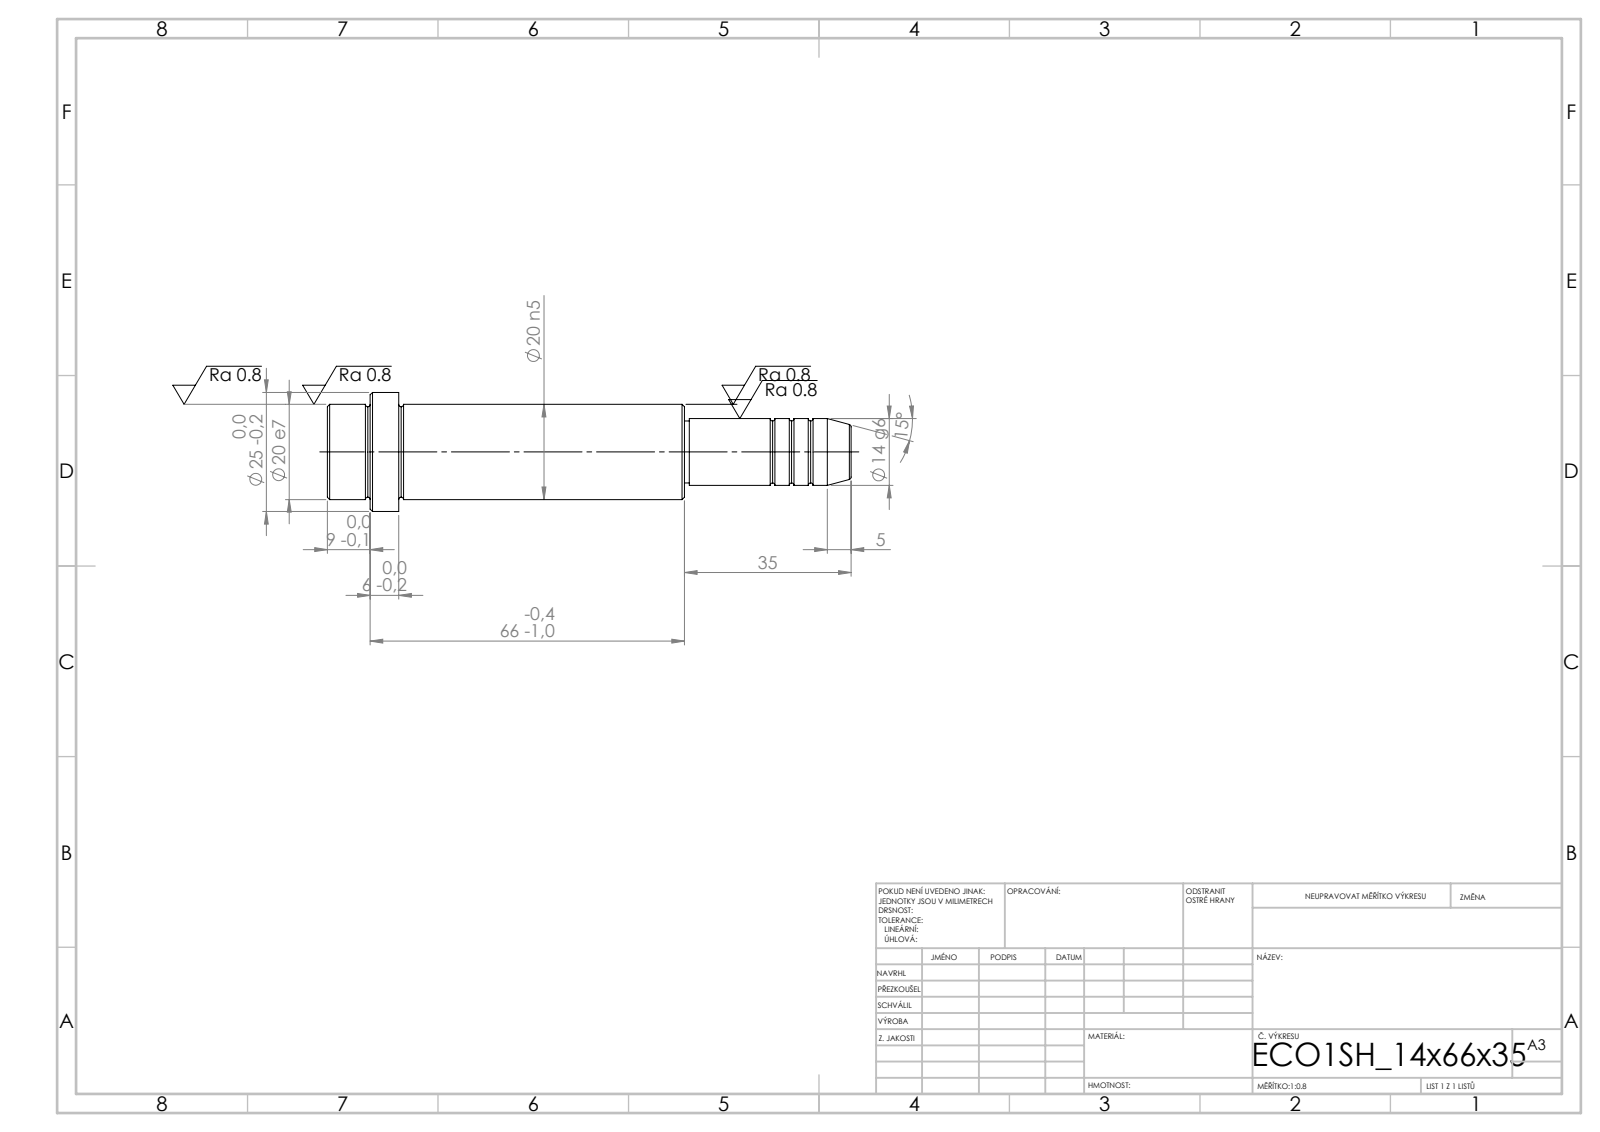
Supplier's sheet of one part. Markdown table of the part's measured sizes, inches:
| quantity | value |
| --- | --- |
| STEP written by | SolidWorks 2019 (CONFIG_CONTROL_DESIGN) |
| units | inches |
| bodies | 1 solid, 52 faces (6 planar, 16 cylindrical, 30 other) |
| overall size | 4.331 × 0.984 × 0.984 |
| volume | 1.814 in³ |
| surface area | 11.42 in² |
| round bosses / shafts (diameter × count) | 0.984 × 1, 0.787 × 1, 0.551 × 1, 0.512 × 1 |
| main face-to-face distances | 0.591, 2.362, 2.953, 2.598, 0.236, 0.354, 1.378, 3.74, 3.976, 4.331 |
